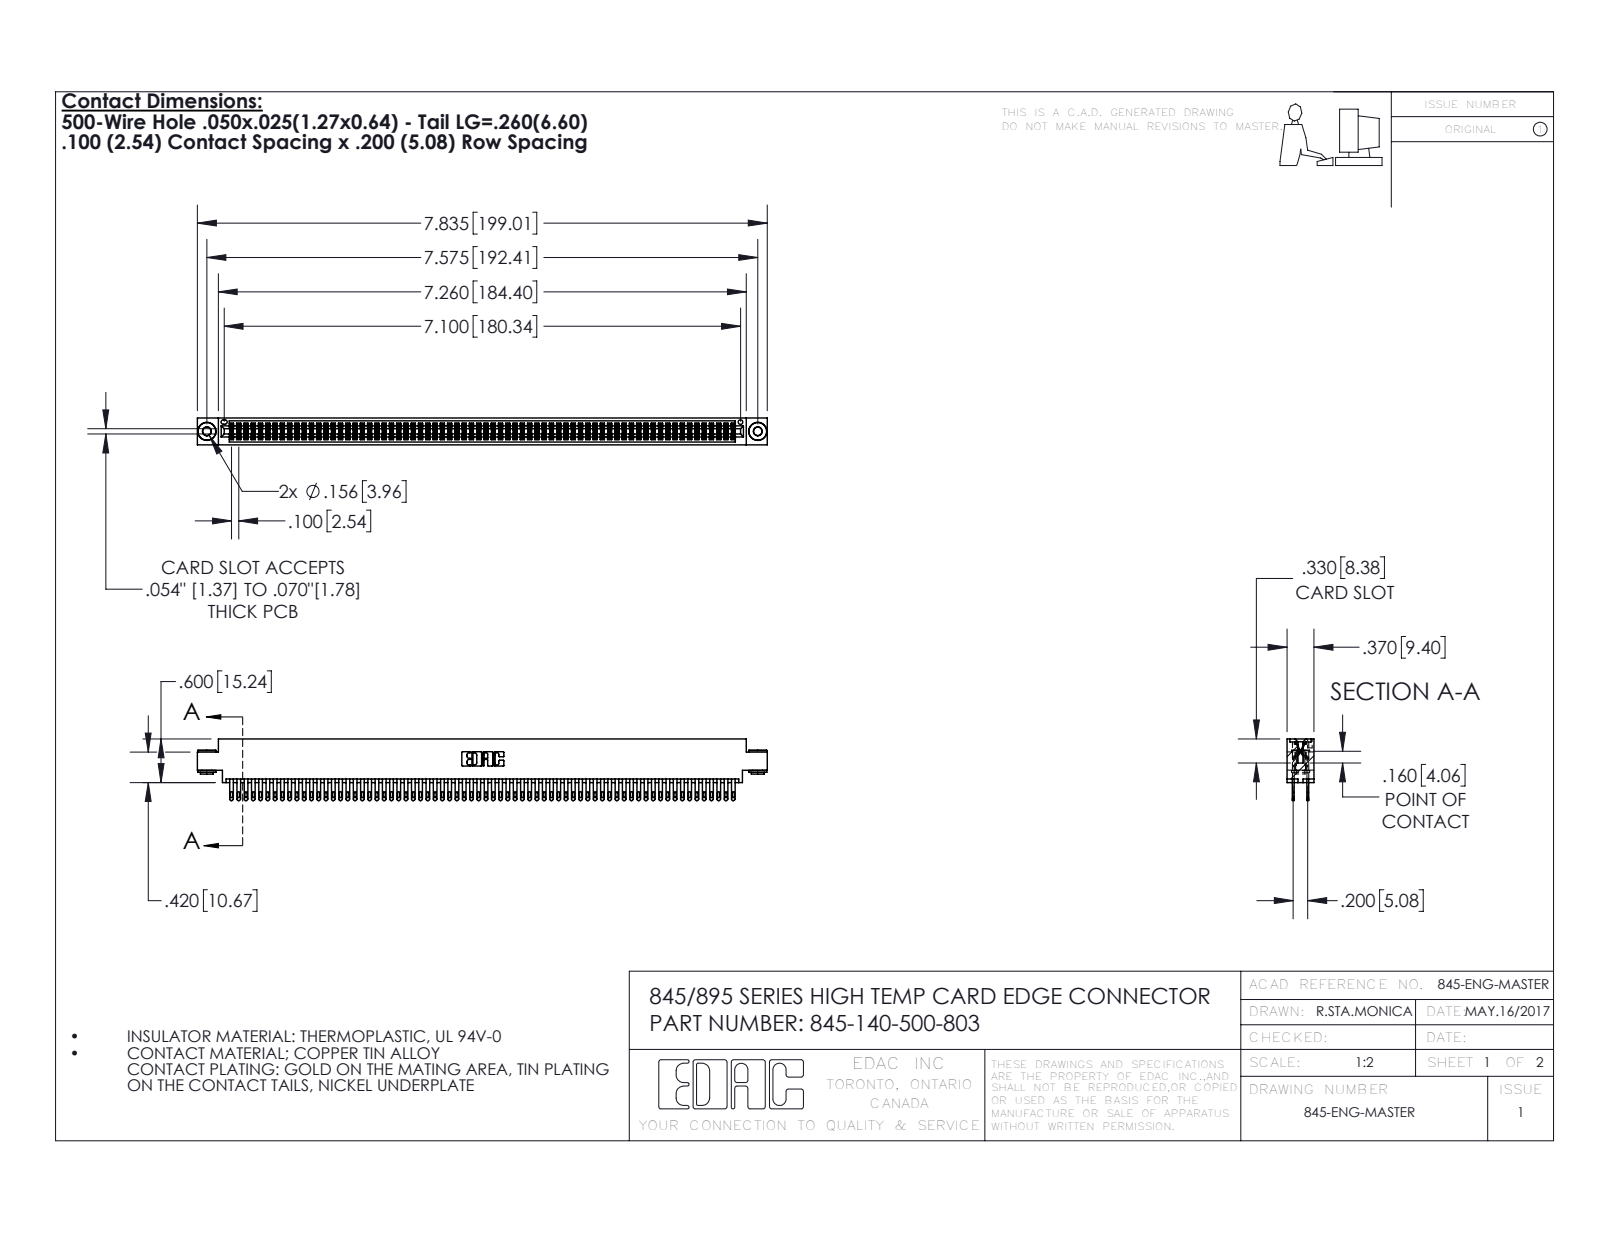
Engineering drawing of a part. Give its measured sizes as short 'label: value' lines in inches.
name: 345-292-001_345-293-100; 345-250-002_345-250-002-102; 345 Part_0.170 Offset - 0.156 Dia-TH; 345-140-500-803
written by: SolidWorks 2016 (CONFIG_CONTROL_DESIGN)
unit: in
bodies: 143 solids, 6608 faces (3874 planar, 2726 cylindrical, 8 other)
size: 7.835 × 0.847 × 0.37
volume: 1.216 in³; area: 49.25 in²
holes: 2× ⌀0.116, 2× ⌀0.156, 1× ⌀0.064
bosses: 2× ⌀0.25, 2× ⌀0.18, 2× ⌀0.136
rounds: 210× R0.006, 140× R0.016, 140× R0.02, 22× R0.01, 6× R0.007, 6× R0.031, 3× R0.026, 2× R0.014
face distances: 0.072, 0.298, 0.2, 0.098, 0.272, 0.025, 0.37, 0.225, 0.175, 0.149
hole spacings: 0.27, 7.339, 7.575
